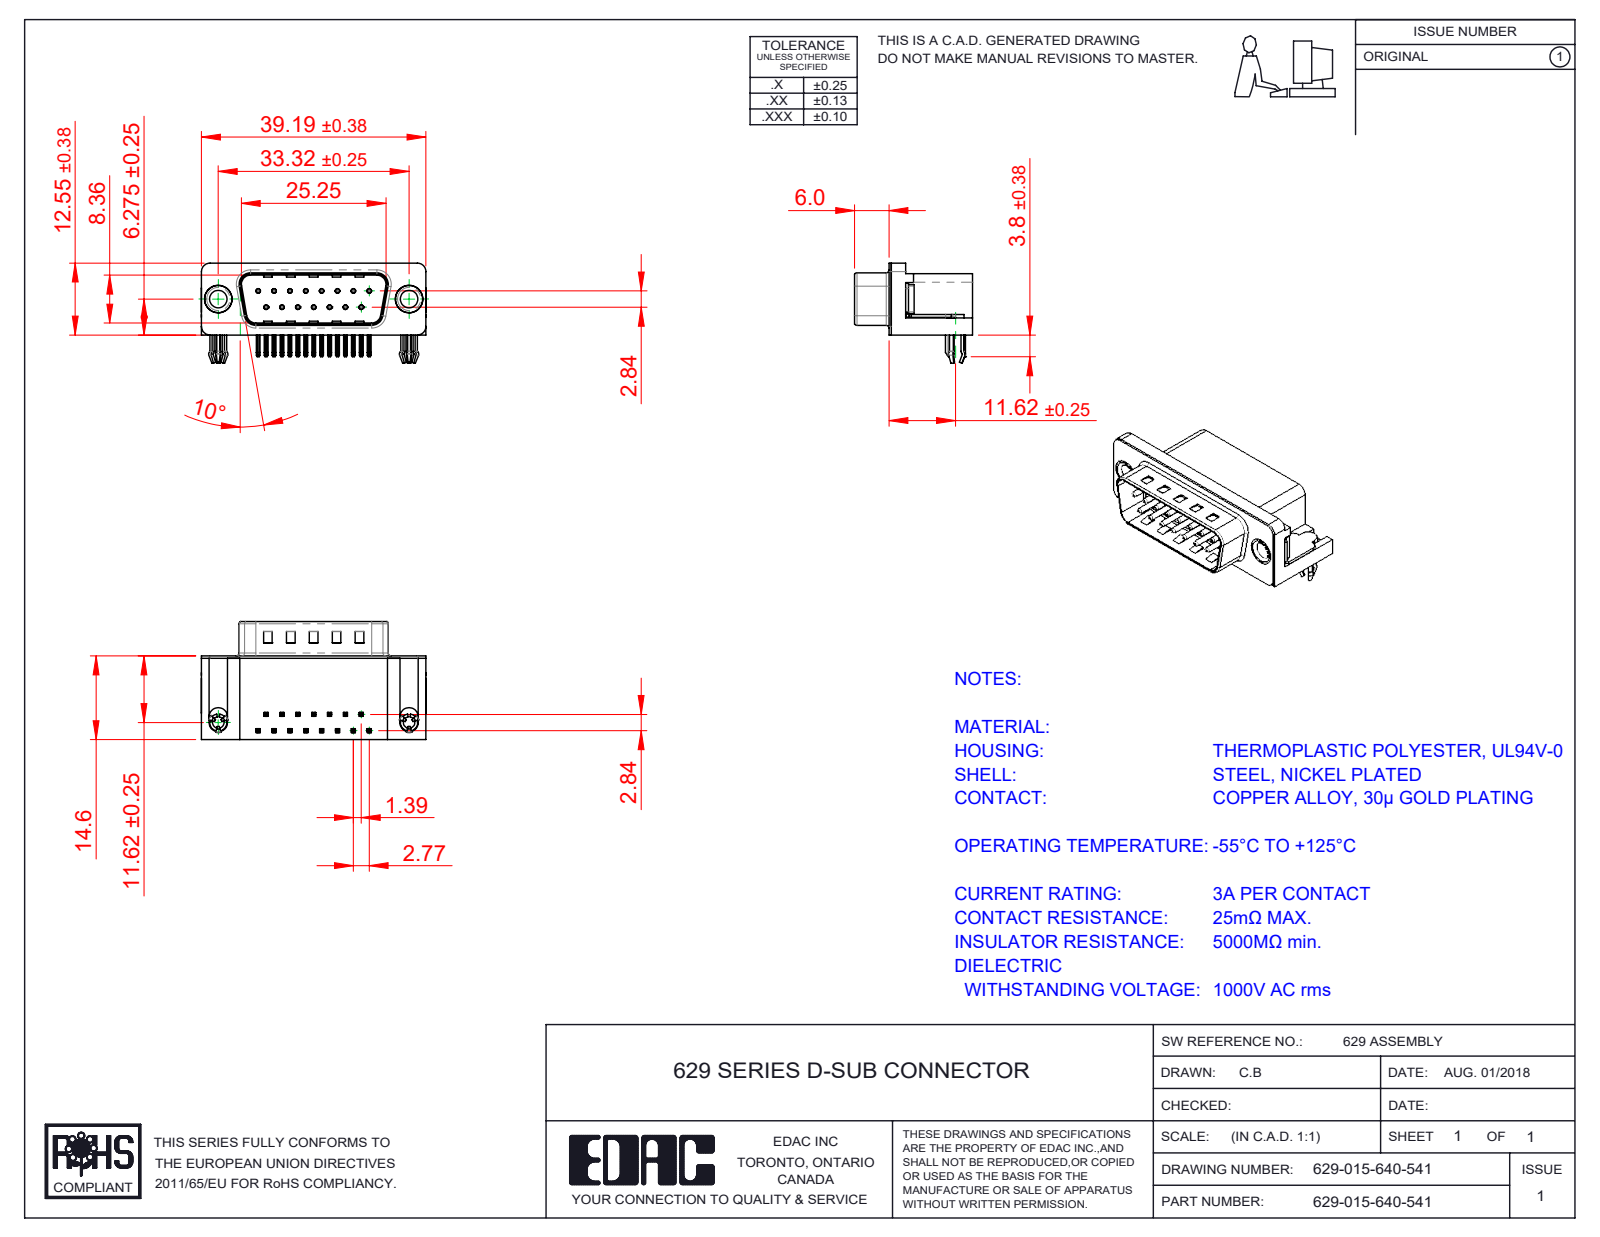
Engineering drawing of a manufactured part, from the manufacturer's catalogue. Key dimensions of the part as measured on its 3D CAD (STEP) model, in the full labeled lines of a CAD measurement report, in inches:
Part name (STEP PRODUCT): 629 Thru Hole Rivet; 629 Contact Bottom; 629 Contact Top; 629 Housing_15 Socket (+3 more)
STEP written by: SolidWorks 2020 (CONFIG_CONTROL_DESIGN)
Units: inches
Bodies: 21 solids, 1539 faces (929 planar, 433 cylindrical, 177 other)
Overall size (bounding box): 1.544 × 0.811 × 0.688
Volume: 0.31 in³ · Surface area: 9.471 in²
Round holes (diameter × count): ⌀0.014 ×15, ⌀0.031 ×15, ⌀0.079 ×2, ⌀0.12 ×2, ⌀0.157 ×2, ⌀0.189 ×2, ⌀0.197 ×2
Round bosses / shafts (diameter × count): ⌀0.03 ×15, ⌀0.193 ×2, ⌀0.187 ×2, ⌀0.152 ×2, ⌀0.118 ×2
Partial cylindrical surfaces — rounded edges, fillets, slot ends (radius × count): R0.01 ×72, R0.005 ×30, R0.039 ×16, R0.02 ×9, R0.063 ×8, R0.059 ×6, R0.035 ×4, R0.079 ×4
Main face-to-face distances: 0.016, 0.559, 0.407, 0.083, 0.575, 0.412, 0.067, 0.428, 0.345, 0.114
Hole centre spacings: 0.124, 0.109, 0.218, 0.327, 0.436, 0.198, 0.198, 0.294
